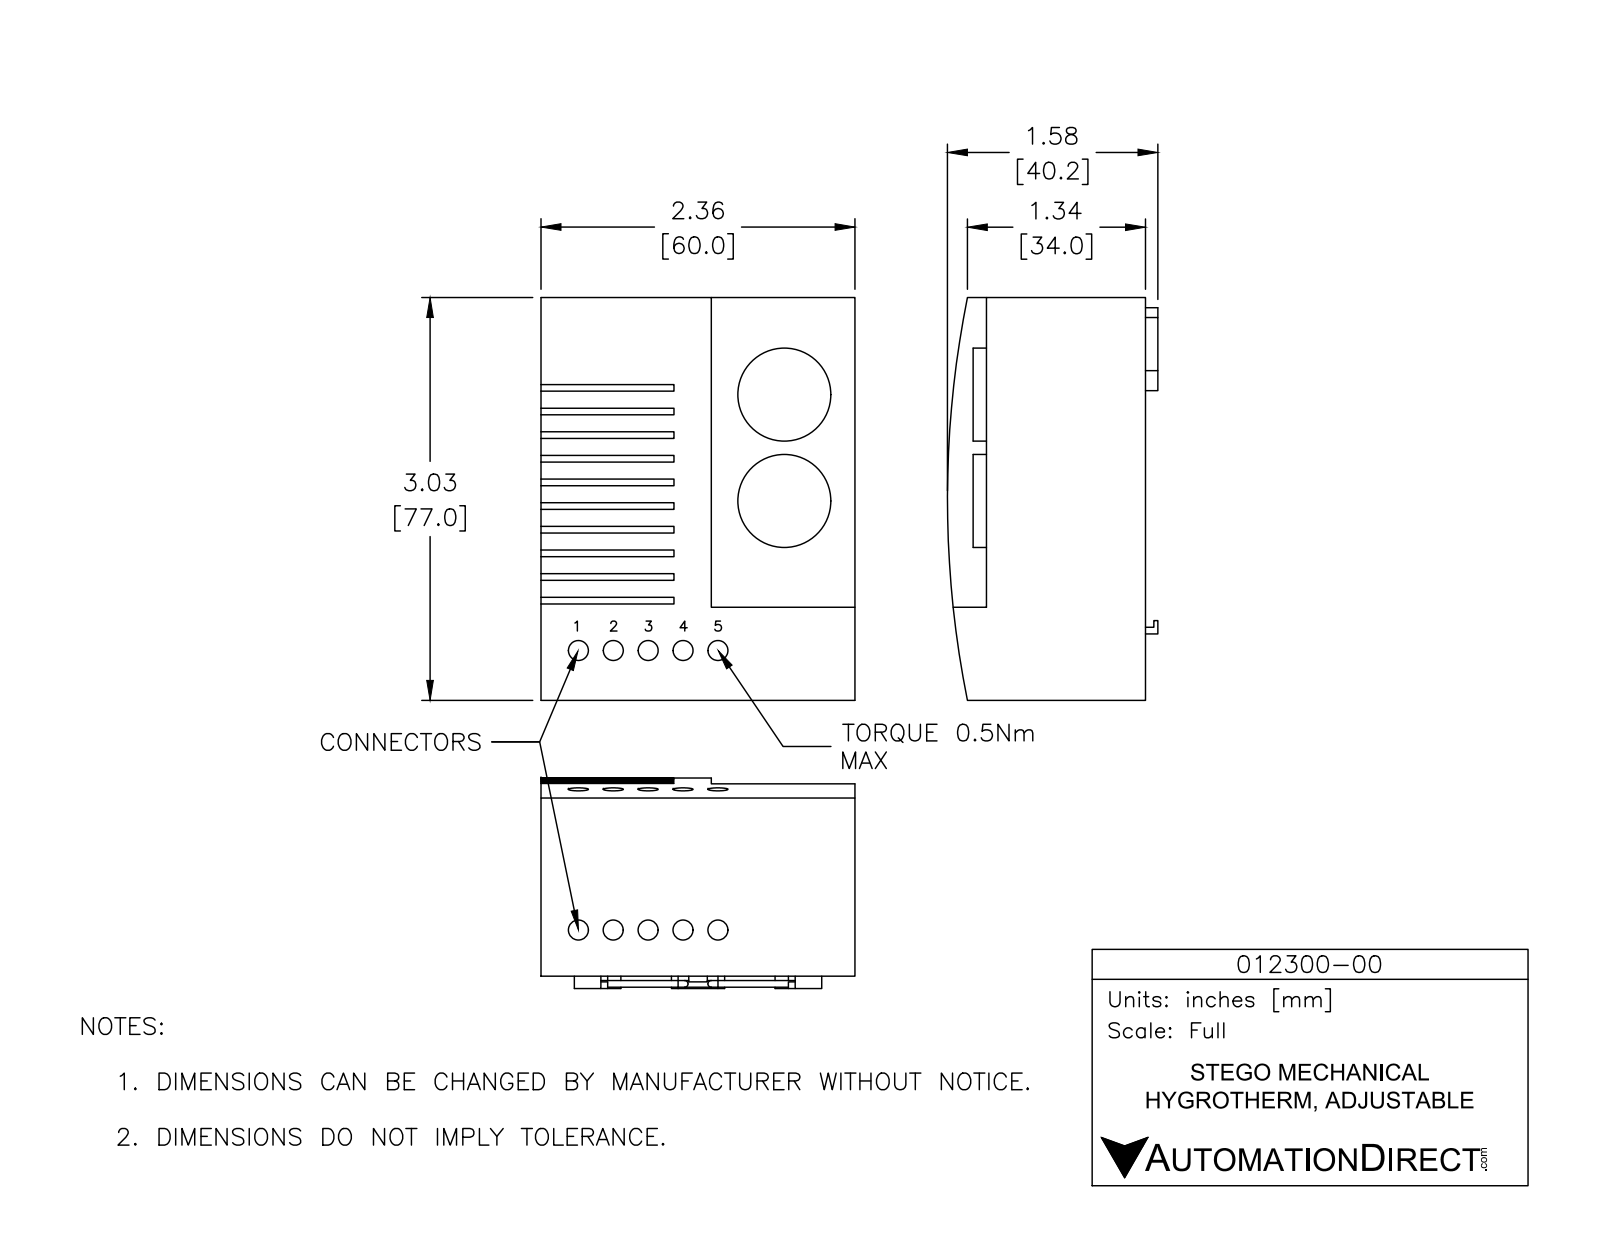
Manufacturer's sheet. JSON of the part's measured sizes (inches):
{"part_name": "PRODUCT_NAME_1", "step_written_by": "ACIS (AUTOMOTIVE_DESIGN_CC2)", "units": "inches", "bodies": {"solids": 1, "faces": 153, "planar": 111, "cylindrical": 36, "other": 6}, "overall_size": [3.03, 2.362, 1.583], "volume_in3": 9.457, "surface_area_in2": 43.41, "round_holes": [[0.15, 10]], "round_bosses_or_shafts": [[0.05, 3], [0.7, 2]], "partial_cylinders_radius": [[0.07, 1], [0.15, 1], [0.2, 1], [7.726, 1]], "face_to_face_distances": [0.178, 0.356, 0.05, 0.711, 0.889, 0.128, 0.228, 2.362, 0.533, 0.534], "hole_center_spacings": [0.263, 0.525, 0.787, 0.262, 0.525, 1.05]}
